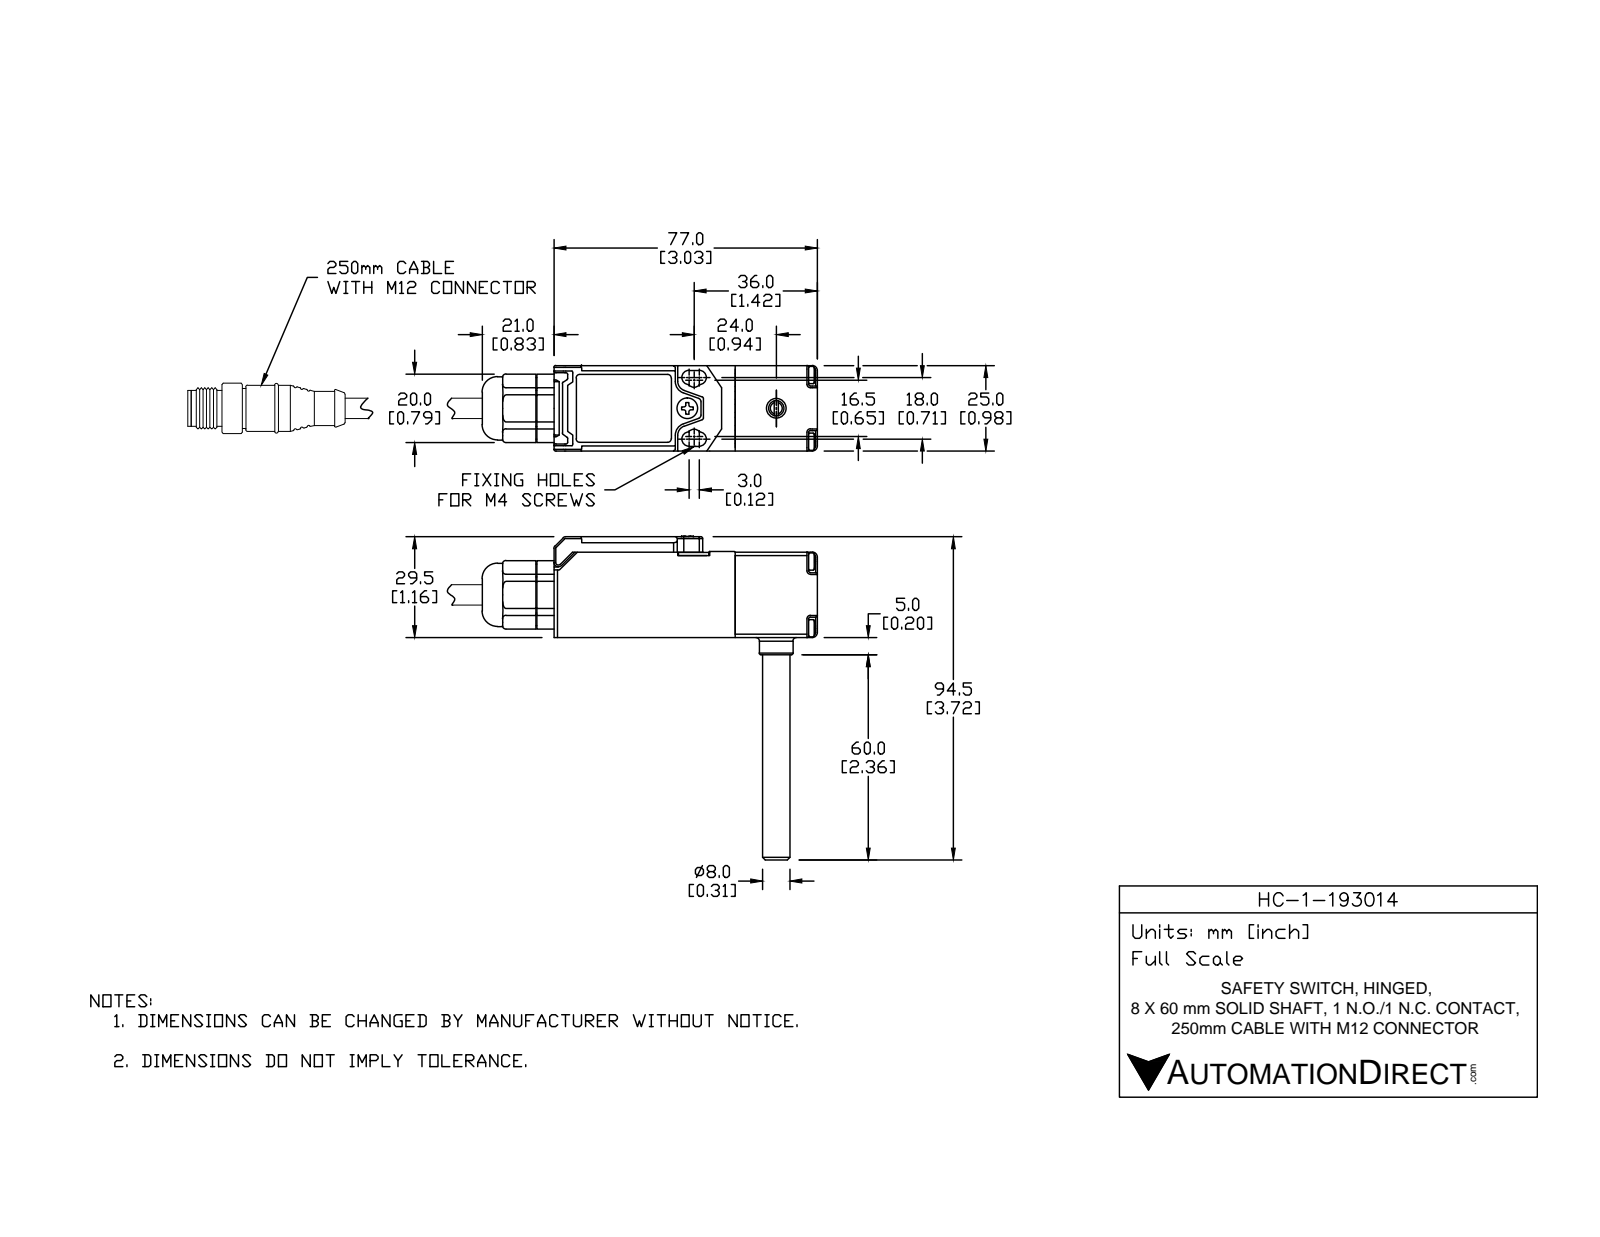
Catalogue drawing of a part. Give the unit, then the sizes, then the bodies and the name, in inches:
Units: inches
Overall size (bounding box): 3.73 × 3.169 × 0.984
Round holes (diameter × count): ⌀0.126 ×5, ⌀0.094 ×4, ⌀0.059 ×2, ⌀0.063 ×2, ⌀0.071 ×2, ⌀0.087 ×2, ⌀0.142 ×2, ⌀0.055 ×1, ⌀0.081 ×1, ⌀0.098 ×1, ⌀0.102 ×1, ⌀0.185 ×1
Round bosses / shafts (diameter × count): ⌀0.102 ×5, ⌀0.197 ×4, ⌀0.079 ×4, ⌀0.138 ×2, ⌀0.74 ×1, ⌀0.531 ×1, ⌀0.386 ×1, ⌀0.315 ×1
Partial cylindrical surfaces — rounded edges, fillets, slot ends (radius × count): R0.02 ×226, R0.004 ×24, R0.012 ×20, R0.039 ×20, R0.059 ×7, R0.083 ×6, R0.11 ×6, R0.008 ×4
Main face-to-face distances: 0.984, 0.079, 0.071, 0.913, 0.039, 0.906, 0.945, 0.827, 0.874, 1.15
Hole centre spacings: 0.543, 0.768, 0.171, 0.187, 0.245, 0.414, 0.423, 0.426
Volume: 1.733 in³ · Surface area: 42.86 in²
Bodies: 14 solids, 1706 faces (700 planar, 601 cylindrical, 405 other)
Part name (STEP PRODUCT): HC-1-193014
STEP written by: SolidWorks 2014 (AUTOMOTIVE_DESIGN)
